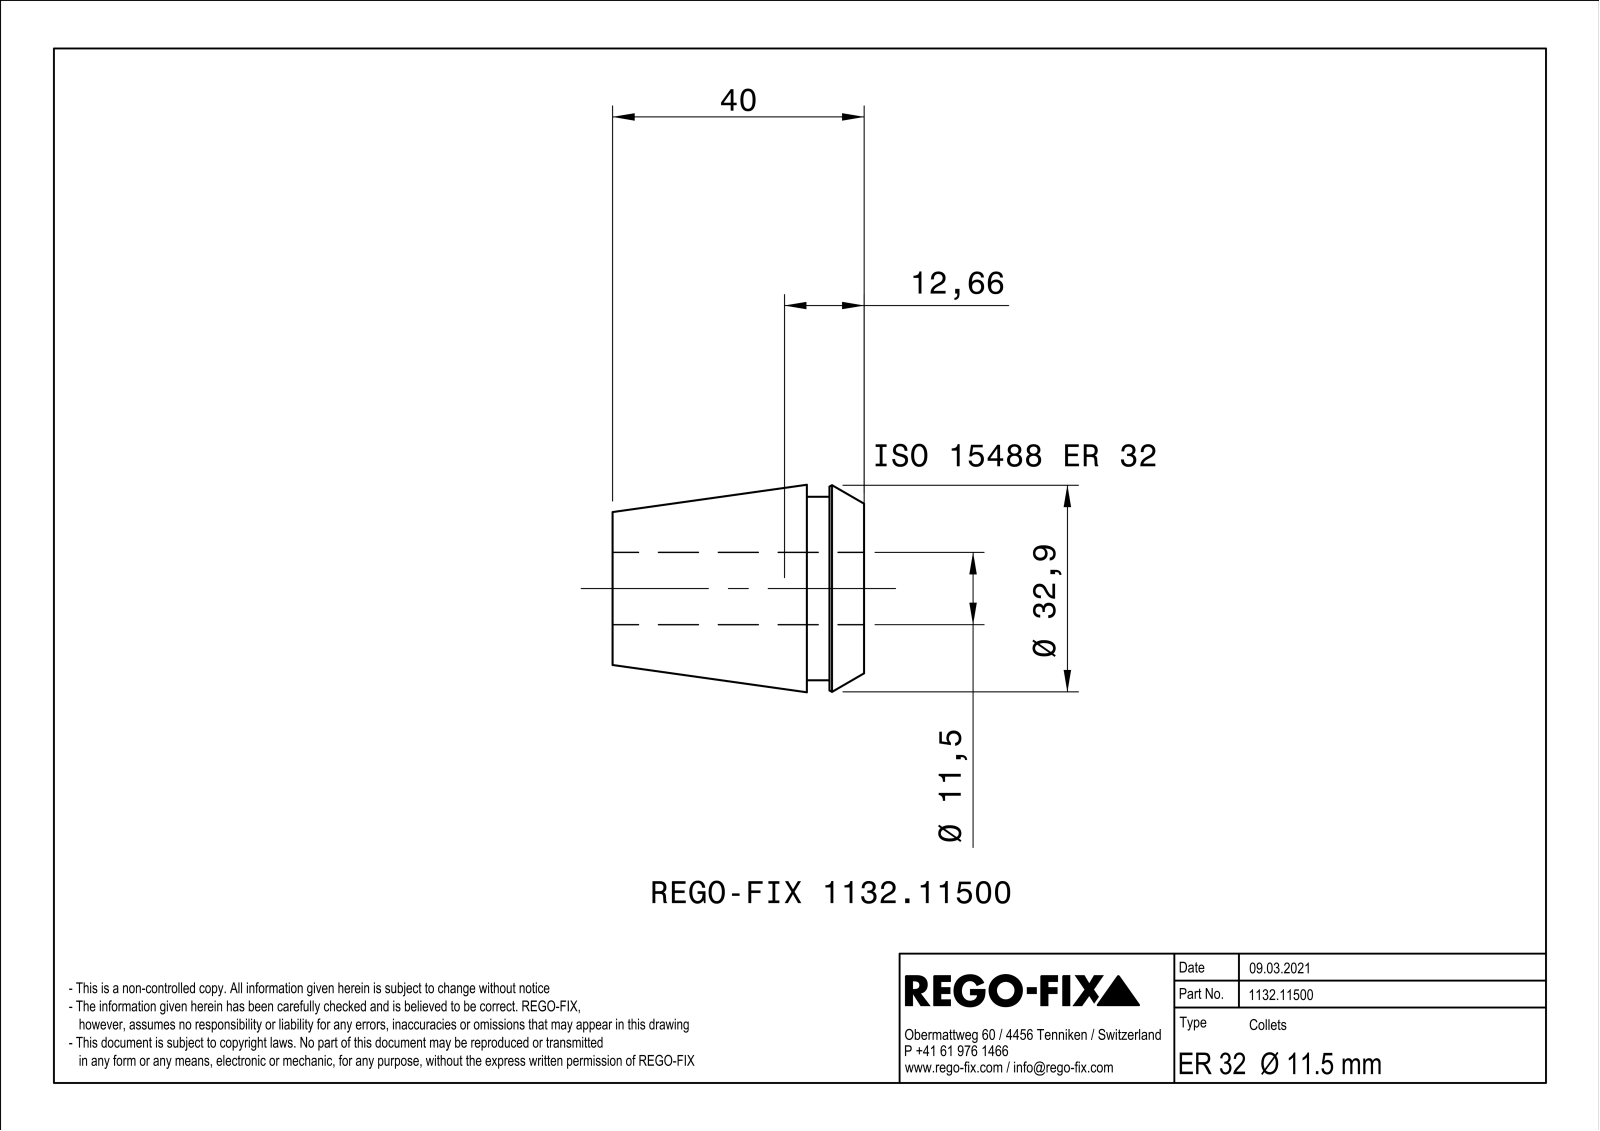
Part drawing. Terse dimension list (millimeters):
name: NOCUT
written by: SIEMENS PLM Software Solid Edge ST10 (AUTOMOTIVE_DESIGN)
unit: mm
bodies: 1 solid, 209 faces (88 planar, 41 cylindrical, 80 other)
size: 40 × 32.98 × 32.98
volume: 17 315 mm³; area: 15 059 mm²
holes: 1× ⌀11.5
bosses: 1× ⌀29.2
rounds: 20× R0.4
face distances: 1, 40, 9.1, 30.9, 5.5, 3.6, 34.5, 6, 0.5, 3.1
